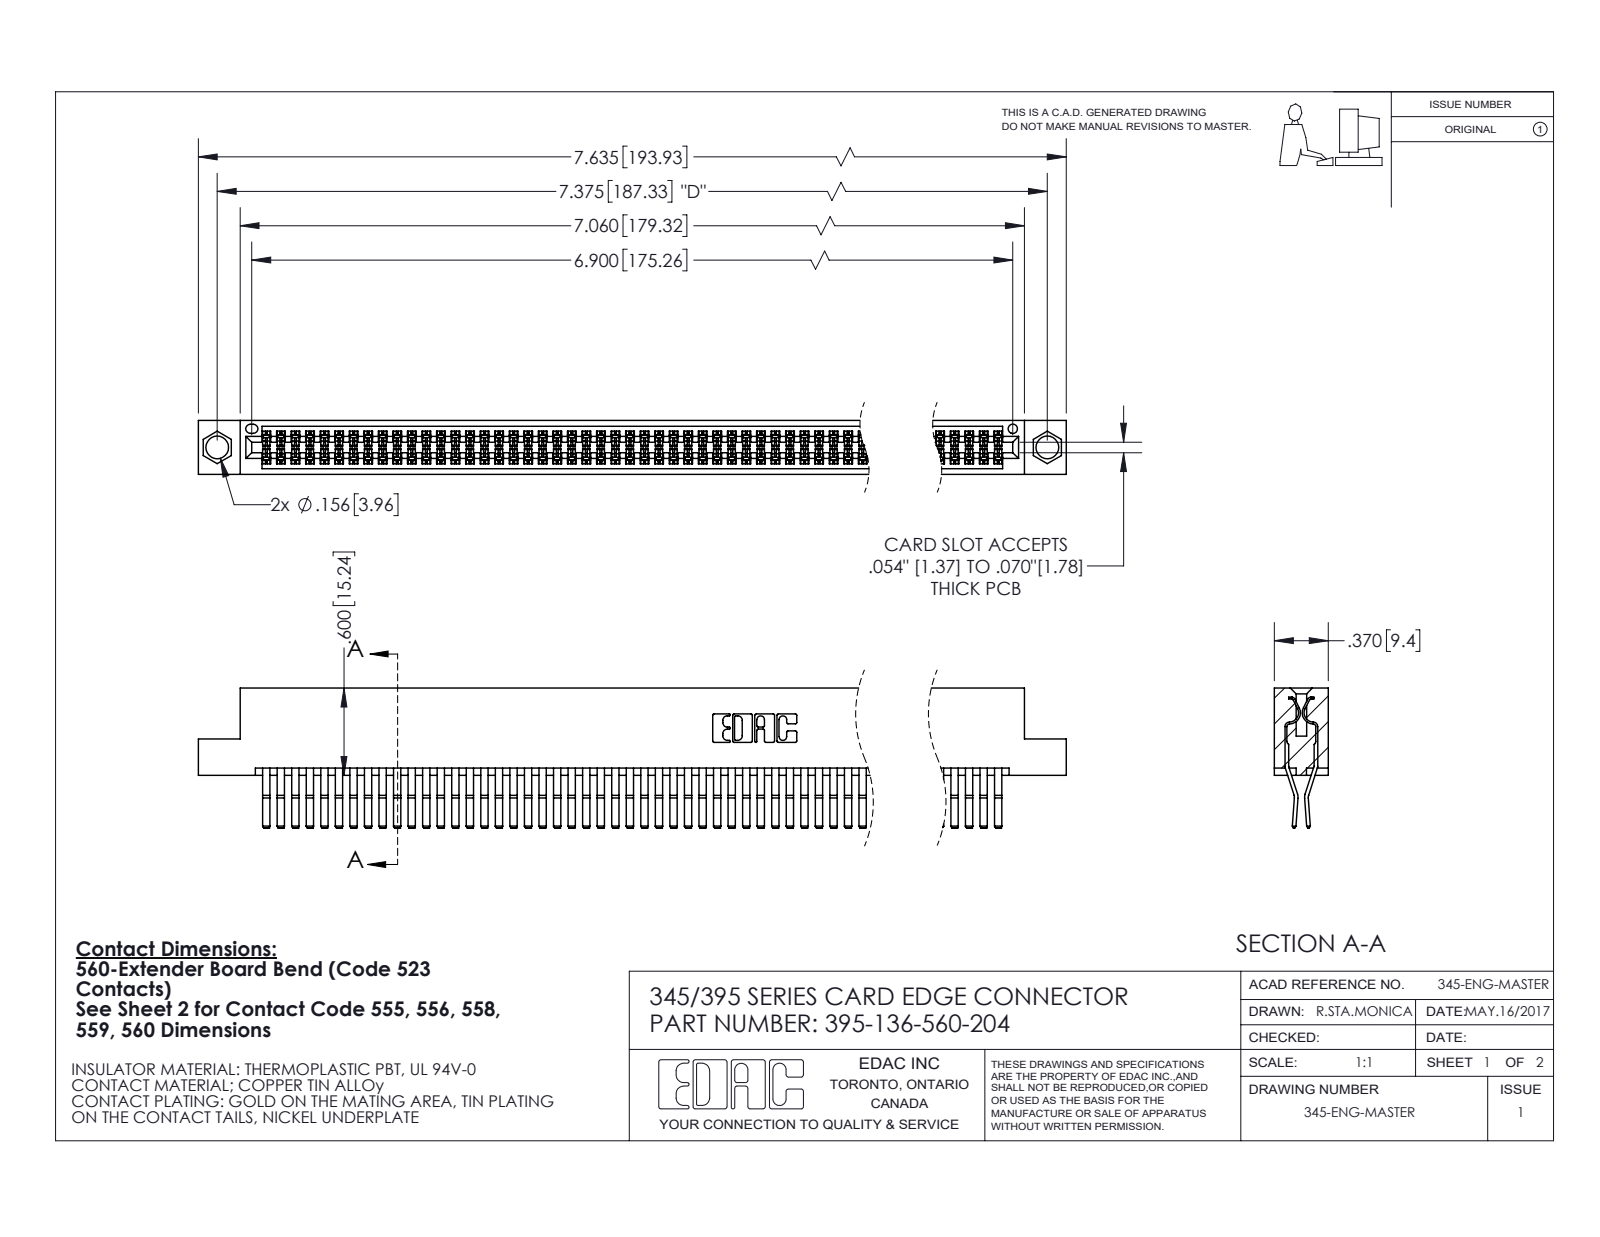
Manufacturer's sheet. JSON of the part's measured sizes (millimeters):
{"part_name": "395-136-560-204; 345-292-001_560 Tail; 345 Part_Flush Mounting Lugs - 0.156 Dia-TI", "step_written_by": "SolidWorks 2020 (CONFIG_CONTROL_DESIGN)", "units": "millimeters", "bodies": {"solids": 137, "faces": 7212, "planar": 4582, "cylindrical": 2630, "other": 0}, "overall_size": [193.9, 24.4, 9.4], "volume_mm3": 19860, "surface_area_mm2": 32010, "round_holes": [[4, 2], [1.6, 1]], "partial_cylinders_radius": [[0.2, 204], [0.3, 22], [0.2, 6], [0.8, 6], [0.7, 3], [0.3, 2], [0.4, 2], [0.5, 2]], "face_to_face_distances": [0.6, 7.6, 1.8, 9.4, 5.1, 2.5, 6.9, 5.7, 4.4, 3.8], "hole_center_spacings": [6.9, 181.3, 187.3]}
